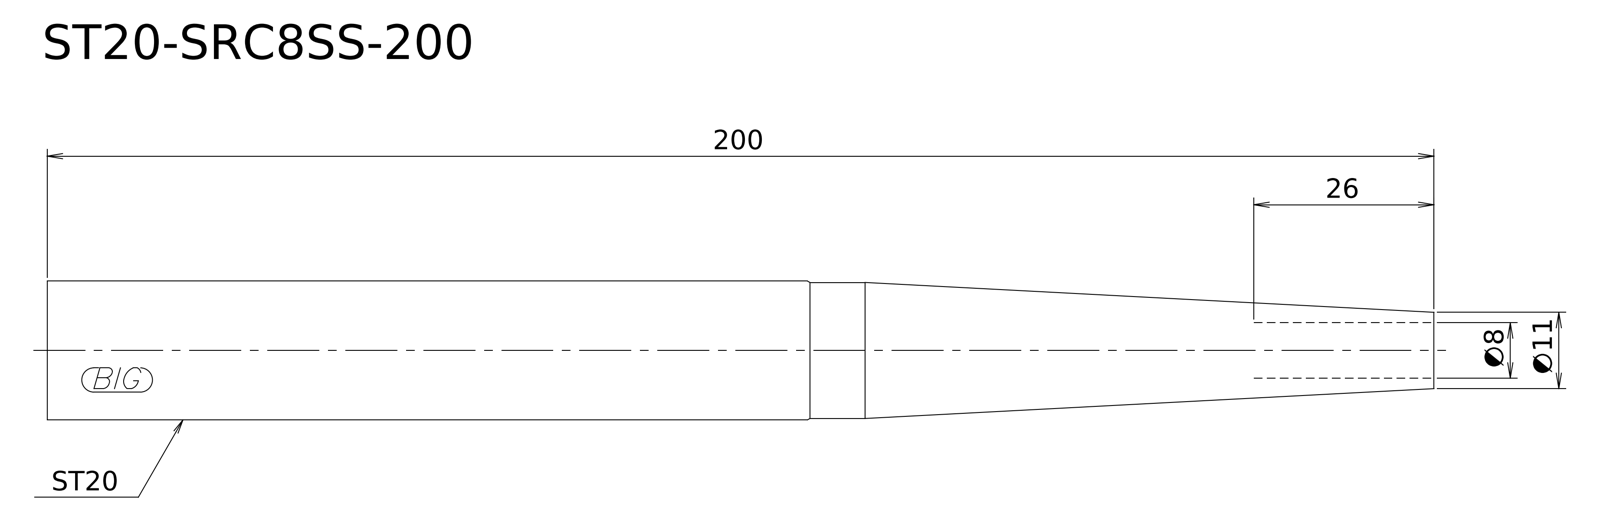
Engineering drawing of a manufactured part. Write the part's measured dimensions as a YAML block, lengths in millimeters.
step_written_by: "Kubotek KeyCreator V8.5.1 (14335) (CONFIG_CONTROL_DESIGN)"
units: millimeters
bodies: {solids: 1, faces: 6, planar: 2, cylindrical: 2, other: 2}
overall_size: [200, 20, 20]
volume: 52437
surface_area: 11763
round_bosses_or_shafts:
  - {diameter: 20, count: 1}
  - {diameter: 19.6, count: 1}
face_to_face_distances: [200]
